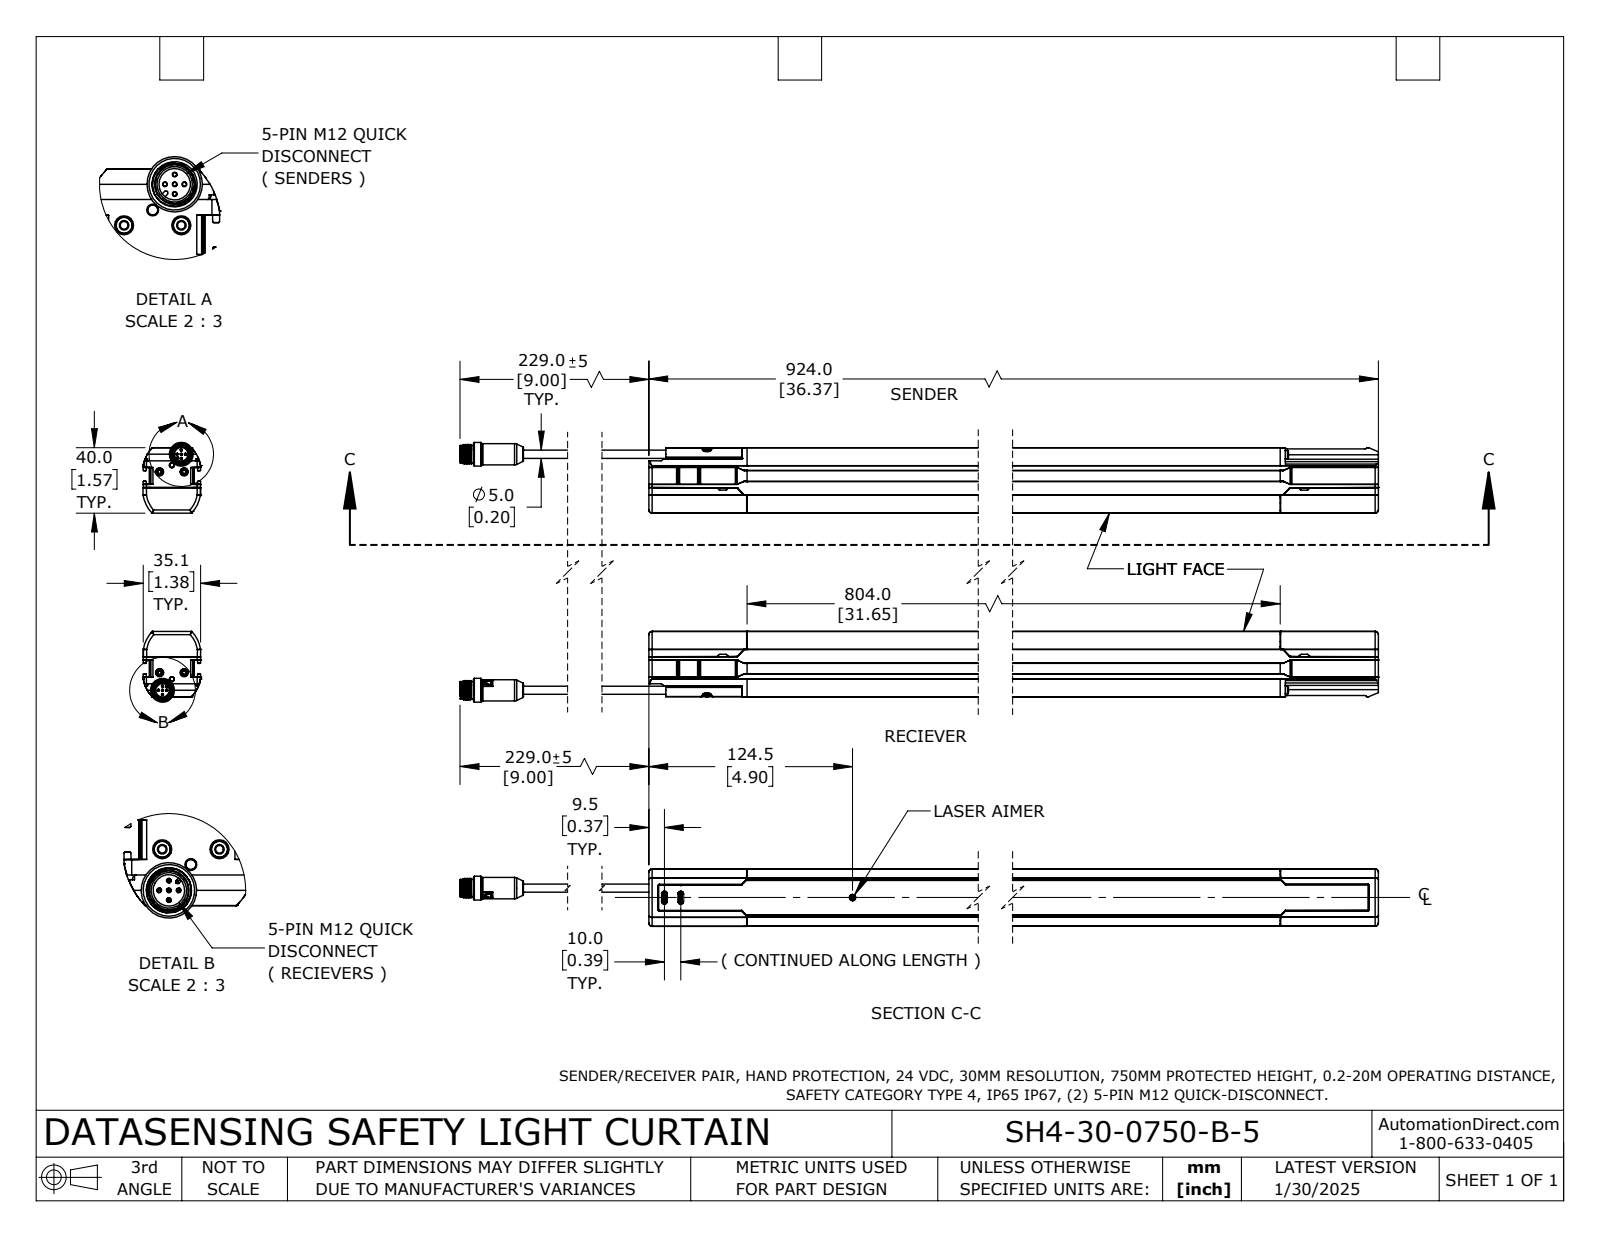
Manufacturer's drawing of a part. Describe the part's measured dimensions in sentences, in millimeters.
The part is named "957920004". Its 3-D file was written by "SolidWorks 2024 (AUTOMOTIVE_DESIGN)". It is 4 solids with 2590 faces: 1186 planar, 778 cylindrical and 626 other. Overall it measures 987.3 by 158.7 by 35.2 millimeters. Its volume is 1 778 000 cubic millimeters and its surface area 329 300 square millimeters. Round holes: 4 of diameter 2, 4 of diameter 3, 4 of diameter 5, 2 of diameter 2.5, 2 of diameter 2.6, 2 of diameter 2.6, 2 of diameter 2.6, 2 of diameter 2.8, 2 of diameter 8.3, 2 of diameter 9.7, 2 of diameter 10.3, 2 of diameter 10.8. Round bosses or shafts: 10 of diameter 5, 10 of diameter 1, 8 of diameter 2.2, 4 of diameter 4.4, 2 of diameter 14.5, 2 of diameter 13, 2 of diameter 10.6, 2 of diameter 9.5. Partial cylindrical surfaces (rounded edges, fillets, slot ends): 164 of radius 0.3, 66 of radius 0.4, 50 of radius 0.5, 36 of radius 0.2, 20 of radius 0.8, 12 of radius 0.8, 12 of radius 2, 10 of radius 1.5. The main face-to-face distances are 38, 114.2, 4, 31, 76.2, 35, 152.2, 27.1, 26.2, 117.7. The hole center spacings are 22, 137.9, 139.6, 10.9, 15, 17.1, 122.7, 123.6.
